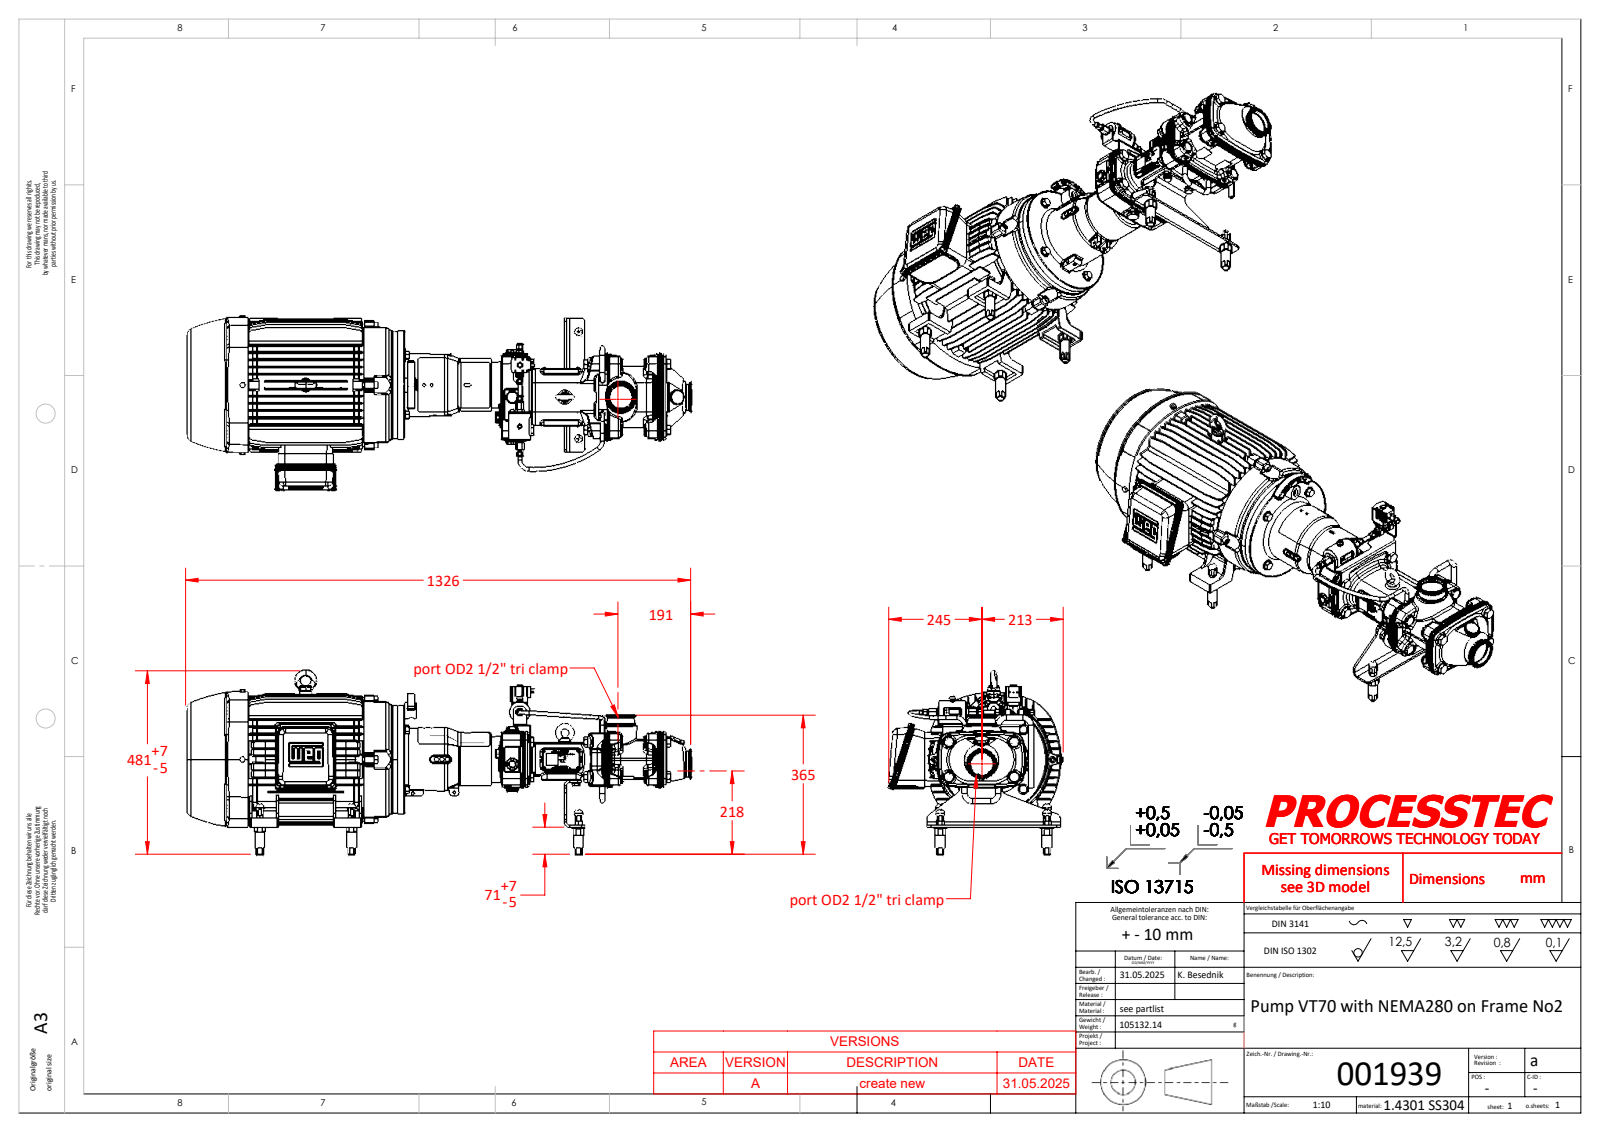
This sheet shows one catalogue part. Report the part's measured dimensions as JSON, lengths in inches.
{"part_name": "001264_ISO 4035 DIN439 - M12; 001031_ISO 4017 - M10 X 25 - A2-70; 001321; 001119 (+8 more)", "step_written_by": "SolidWorks 2023 (AUTOMOTIVE_DESIGN)", "units": "inches", "bodies": {"solids": 115, "faces": 12250, "planar": 5284, "cylindrical": 2198, "other": 4768}, "overall_size": [52.197, 18.949, 18.034], "volume_in3": 3661, "surface_area_in2": 5388, "round_holes": [[0.315, 15], [0.335, 10], [0.551, 10], [0.472, 9], [0.402, 8], [0.236, 7], [0.413, 7], [0.232, 6], [0.283, 6], [0.874, 6], [0.098, 5], [0.591, 5]], "round_bosses_or_shafts": [[0.236, 19], [0.63, 10], [0.394, 10], [0.945, 8], [1.181, 7], [0.866, 7], [0.748, 6], [0.52, 6]], "partial_cylinders_radius": [[0.079, 144], [0.157, 85], [0.118, 76], [0.02, 60], [0.315, 56], [0.197, 44], [0.055, 16], [0.591, 16]], "face_to_face_distances": [12.717, 0.735, 7.448, 1.3, 0.565, 0.206, 26.882, 14.165, 6.694, 6.713], "hole_center_spacings": [6.252, 1.614, 5.732, 0.159, 0.889, 1.772, 2.335, 3.071]}
